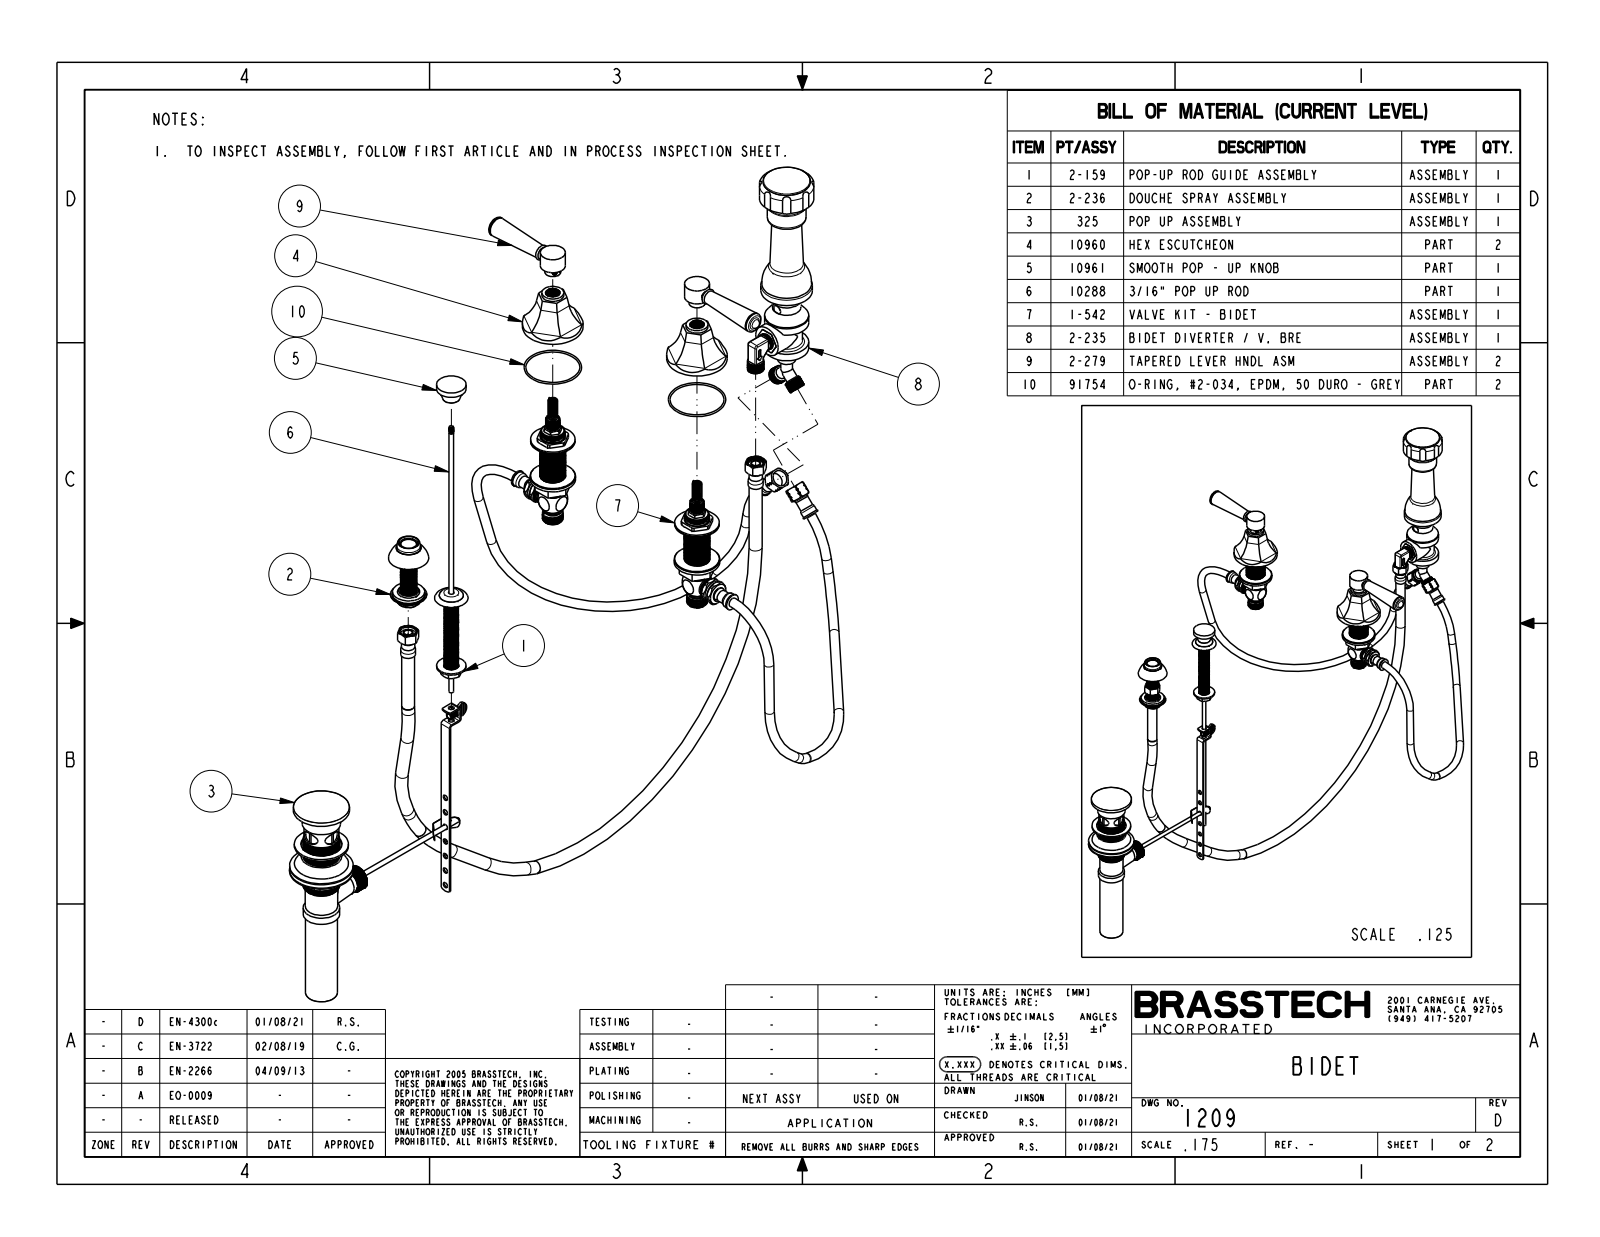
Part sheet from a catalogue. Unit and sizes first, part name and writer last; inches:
Units: inches
Overall size (bounding box): 22.855 × 14.786 × 5.353
Round holes (diameter × count): ⌀0.385 ×1, ⌀0.625 ×1, ⌀0.792 ×1, ⌀0.94 ×1
Round bosses / shafts (diameter × count): ⌀2.375 ×2, ⌀0.98 ×2, ⌀0.86 ×2, ⌀0.625 ×2, ⌀2.025 ×1, ⌀1.52 ×1, ⌀1.16 ×1, ⌀0.925 ×1
Partial cylindrical surfaces — rounded edges, fillets, slot ends (radius × count): R1.541 ×12, R0.21 ×8, R0.357 ×1, R1.077 ×1
Main face-to-face distances: 3.928, 1.957, 3.468, 1.511, 1.527, 0.43, 1.941, 1.647, 0.12, 0.31
Volume: 22.49 in³ · Surface area: 98.82 in²
Bodies: 5 solids, 243 faces (75 planar, 82 cylindrical, 86 other)
Part name (STEP PRODUCT): 1209
STEP written by: CREO PARAMETRIC BY PTC INC, 2018400 (CONFIG_CONTROL_DESIGN)
